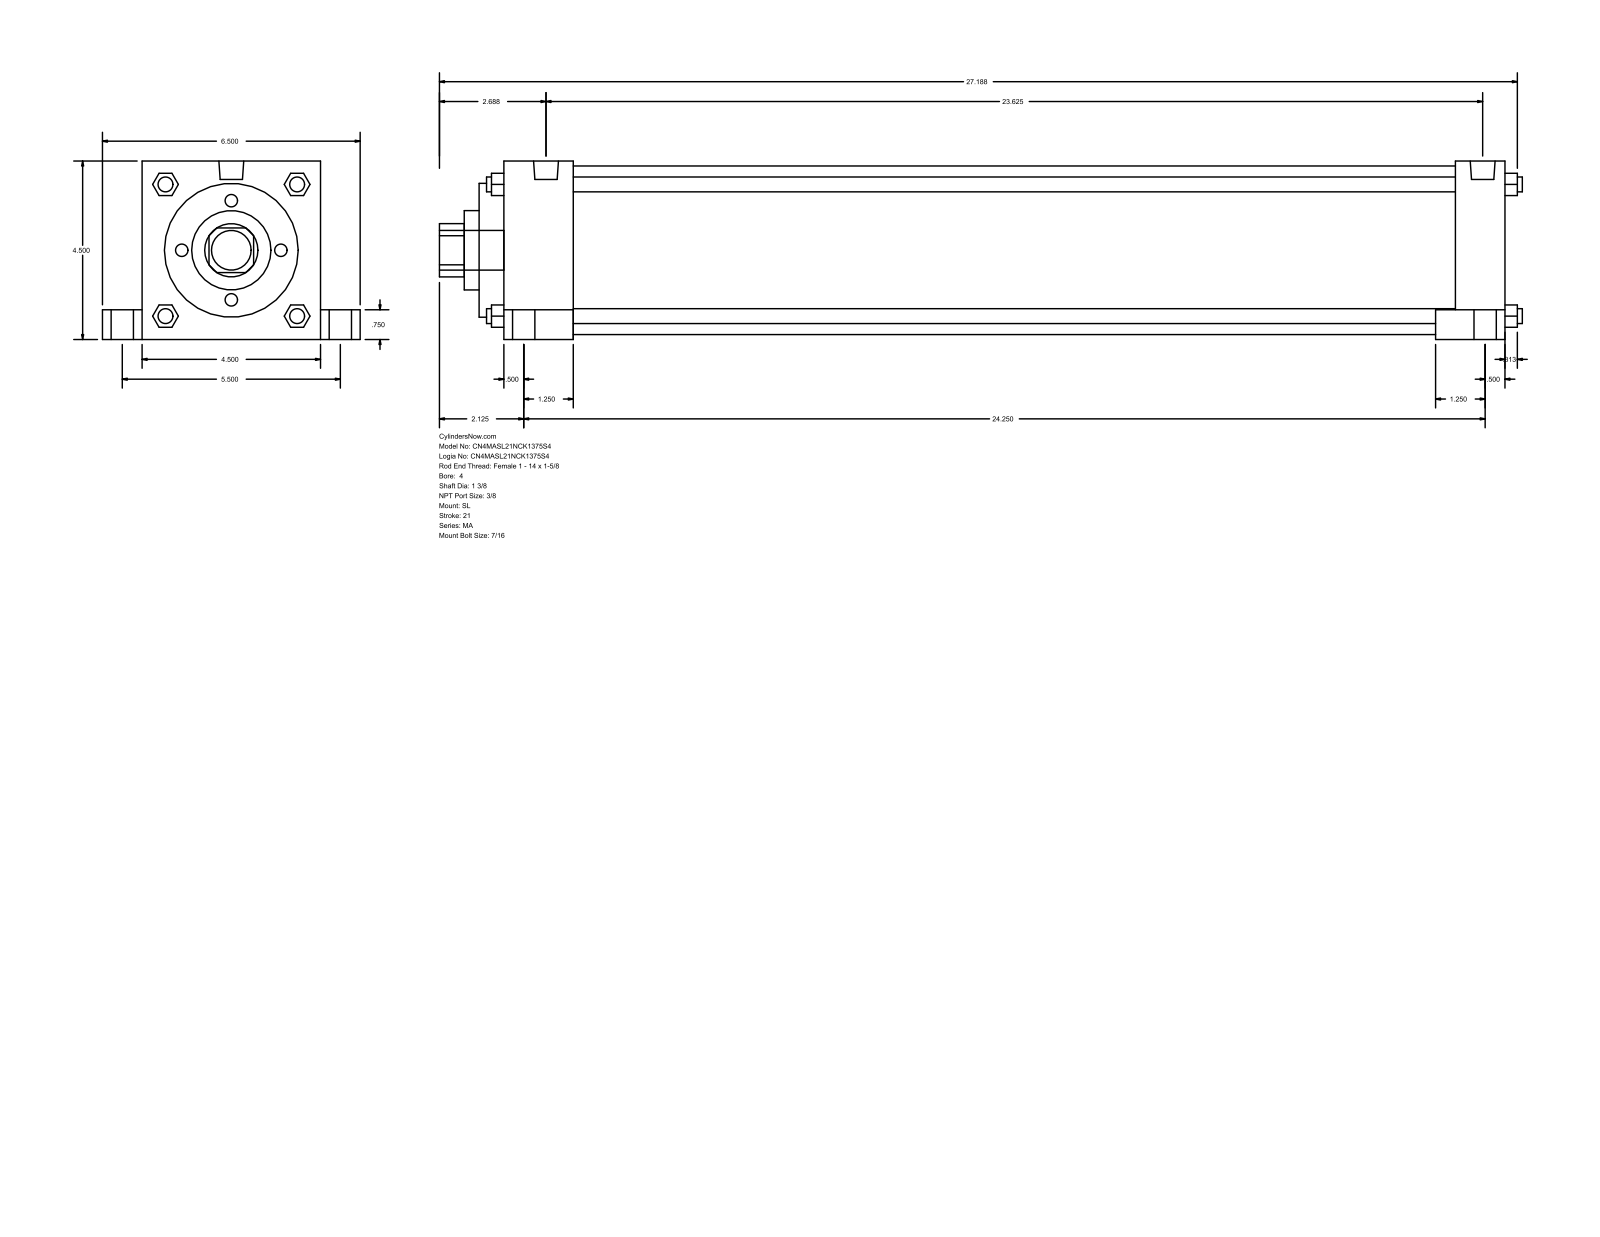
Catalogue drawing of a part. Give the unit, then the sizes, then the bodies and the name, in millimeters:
Units: millimetres
Overall size (bounding box): 693.74 × 165.1 × 114.3
Round holes (diameter × count): ⌀34.92 ×1, ⌀50.8 ×1, ⌀85.72 ×1, ⌀107.95 ×1
Round bosses / shafts (diameter × count): ⌀20.64 ×4, ⌀14.29 ×4, ⌀11.11 ×4, ⌀9.53 ×4, ⌀15.93 ×2, ⌀25.4 ×1
Partial cylindrical surfaces — rounded edges, fillets, slot ends (radius × count): R17.06 ×1
Main face-to-face distances: 114.3, 641.35, 657.22, 15.87, 60.32, 44.45, 596.9, 625.48, 609.61, 565.16
Bodies: 0 solids, 150 faces (113 planar, 37 cylindrical, 0 other)
Part name (STEP PRODUCT): MA_SL__0400_1.375
STEP written by: GSSL Pune (CONFIG_CONTROL_DESIGN)
